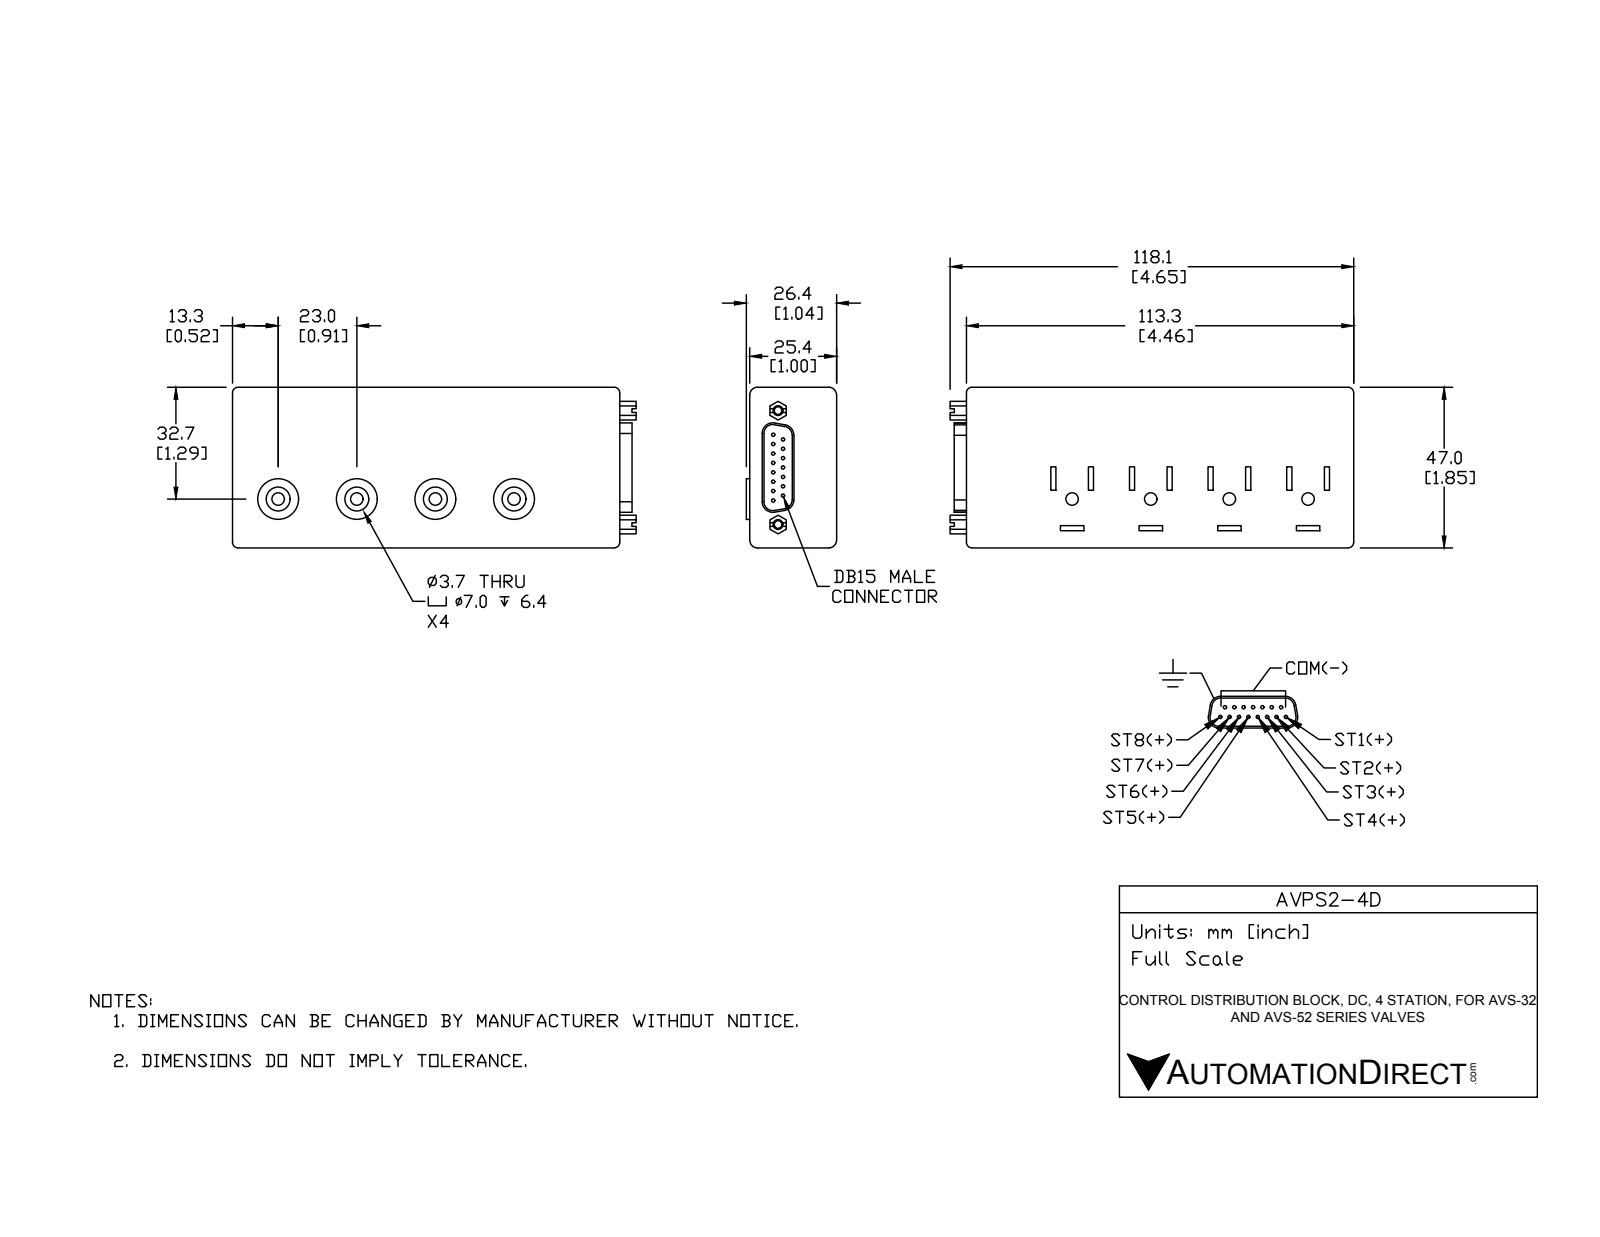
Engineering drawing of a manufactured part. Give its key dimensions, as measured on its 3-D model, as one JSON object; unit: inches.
{"part_name": "AVPS2-4D", "step_written_by": "SolidWorks 2016 (AUTOMOTIVE_DESIGN)", "units": "inches", "bodies": {"solids": 1, "faces": 219, "planar": 127, "cylindrical": 80, "other": 12}, "overall_size": [4.649, 1.85, 1.04], "volume_in3": 8.062, "surface_area_in2": 34.25, "round_holes": [[0.145, 4], [0.275, 4], [0.089, 2]], "round_bosses_or_shafts": [[0.039, 15], [0.469, 4]], "partial_cylinders_radius": [[0.062, 6], [0.09, 4], [0.102, 4], [0.122, 4], [0.063, 2]], "face_to_face_distances": [1, 1.85, 4.46, 0.059, 0.906, 1.812, 0.433, 0.04, 1.04, 0.25], "hole_center_spacings": [0.906, 1.812, 0.906, 1.311, 2.718]}
